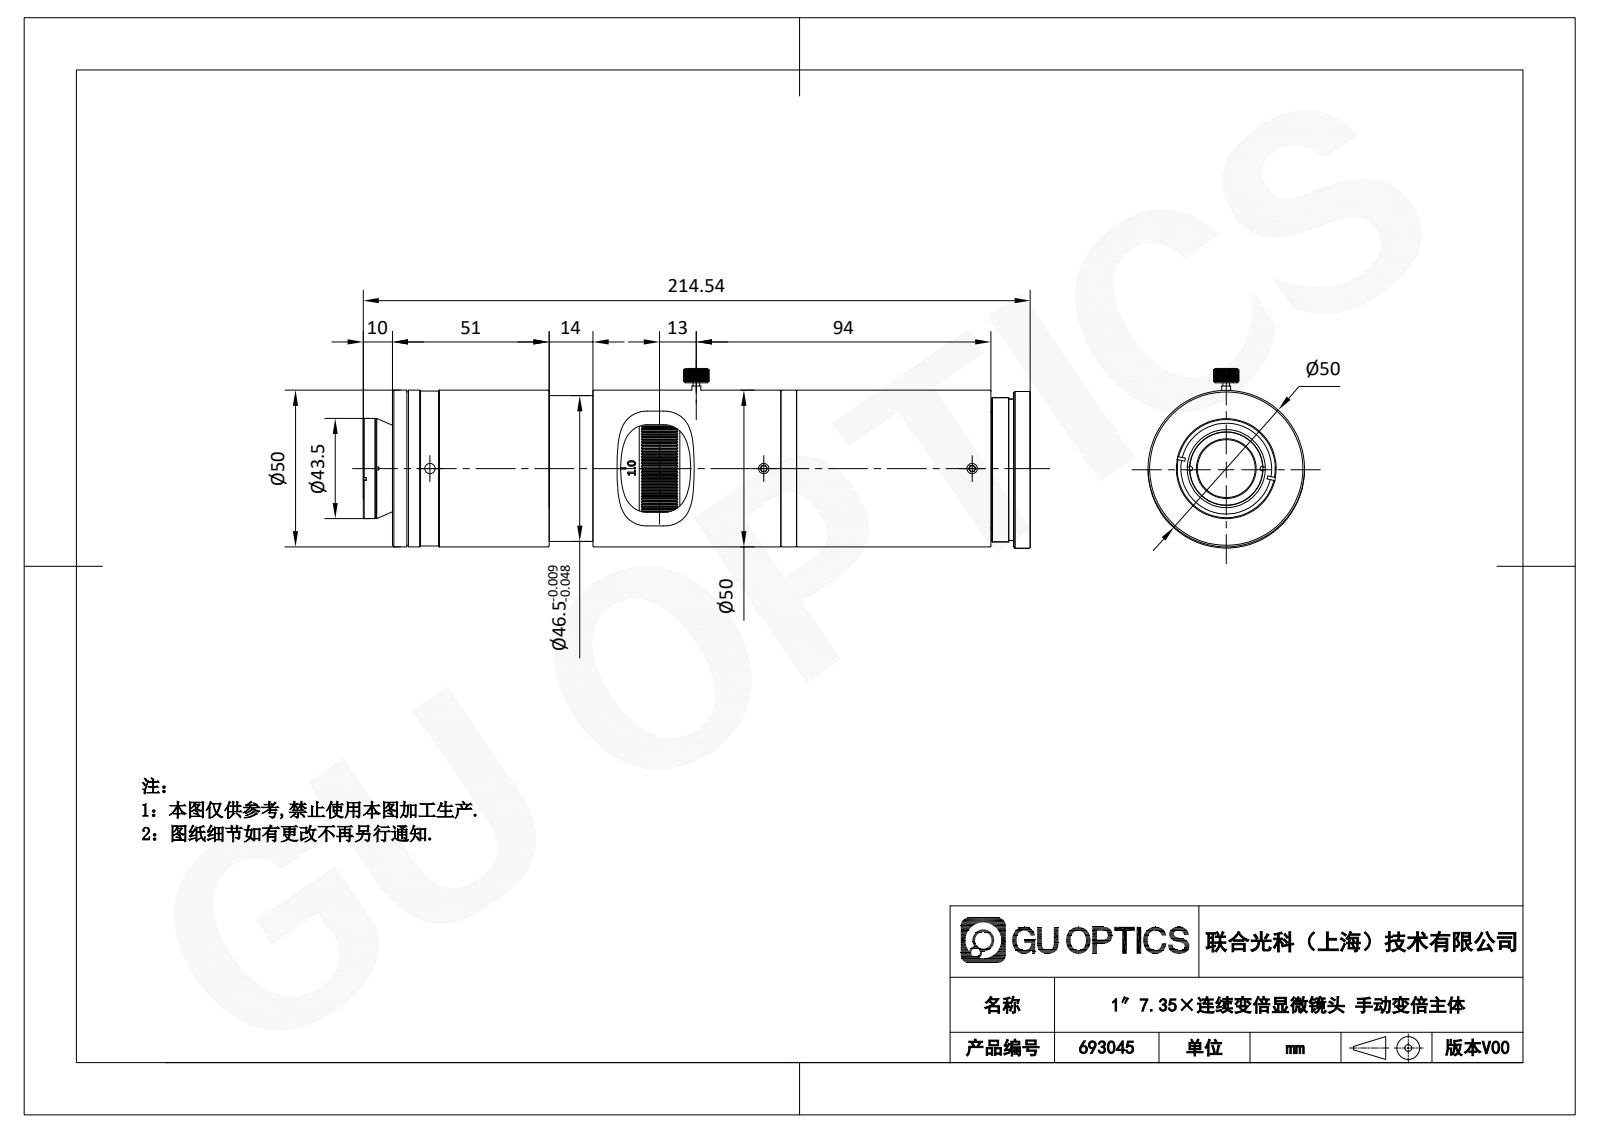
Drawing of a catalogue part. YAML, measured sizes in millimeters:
part_name: "693045"
step_written_by: "SolidWorks 2020 (CONFIG_CONTROL_DESIGN)"
units: millimeters
bodies: {solids: 21, faces: 1470, planar: 731, cylindrical: 369, other: 370}
overall_size: [212.84, 57.35, 50]
volume: 203292
surface_area: 116773
round_holes:
  - {diameter: 3.3, count: 9}
  - {diameter: 2, count: 6}
  - {diameter: 1.6, count: 3}
  - {diameter: 2.4, count: 2}
  - {diameter: 36, count: 2}
  - {diameter: 1.75, count: 1}
  - {diameter: 2.26, count: 1}
  - {diameter: 4.5, count: 1}
  - {diameter: 15.36, count: 1}
  - {diameter: 17.5, count: 1}
  - {diameter: 18.5, count: 1}
  - {diameter: 19.5, count: 1}
round_bosses_or_shafts:
  - {diameter: 4, count: 7}
  - {diameter: 50, count: 2}
  - {diameter: 49.4, count: 1}
  - {diameter: 49, count: 1}
  - {diameter: 46.5, count: 1}
  - {diameter: 46, count: 1}
  - {diameter: 45.1, count: 1}
  - {diameter: 43, count: 1}
partial_cylinders:
  - {radius: 0.6, count: 9}
  - {radius: 0.75, count: 6}
  - {radius: 10, count: 4}
  - {radius: 4, count: 1}
  - {radius: 10.05, count: 1}
  - {radius: 20.49, count: 1}
  - {radius: 24.99, count: 1}
face_to_face_distances: [6, 172.5, 178.5, 5, 8.34, 49.5, 123, 129, 54.5, 118]
hole_center_spacings: [17, 29.44, 20, 23.89, 26.25, 34.64, 35.75, 36.44]
